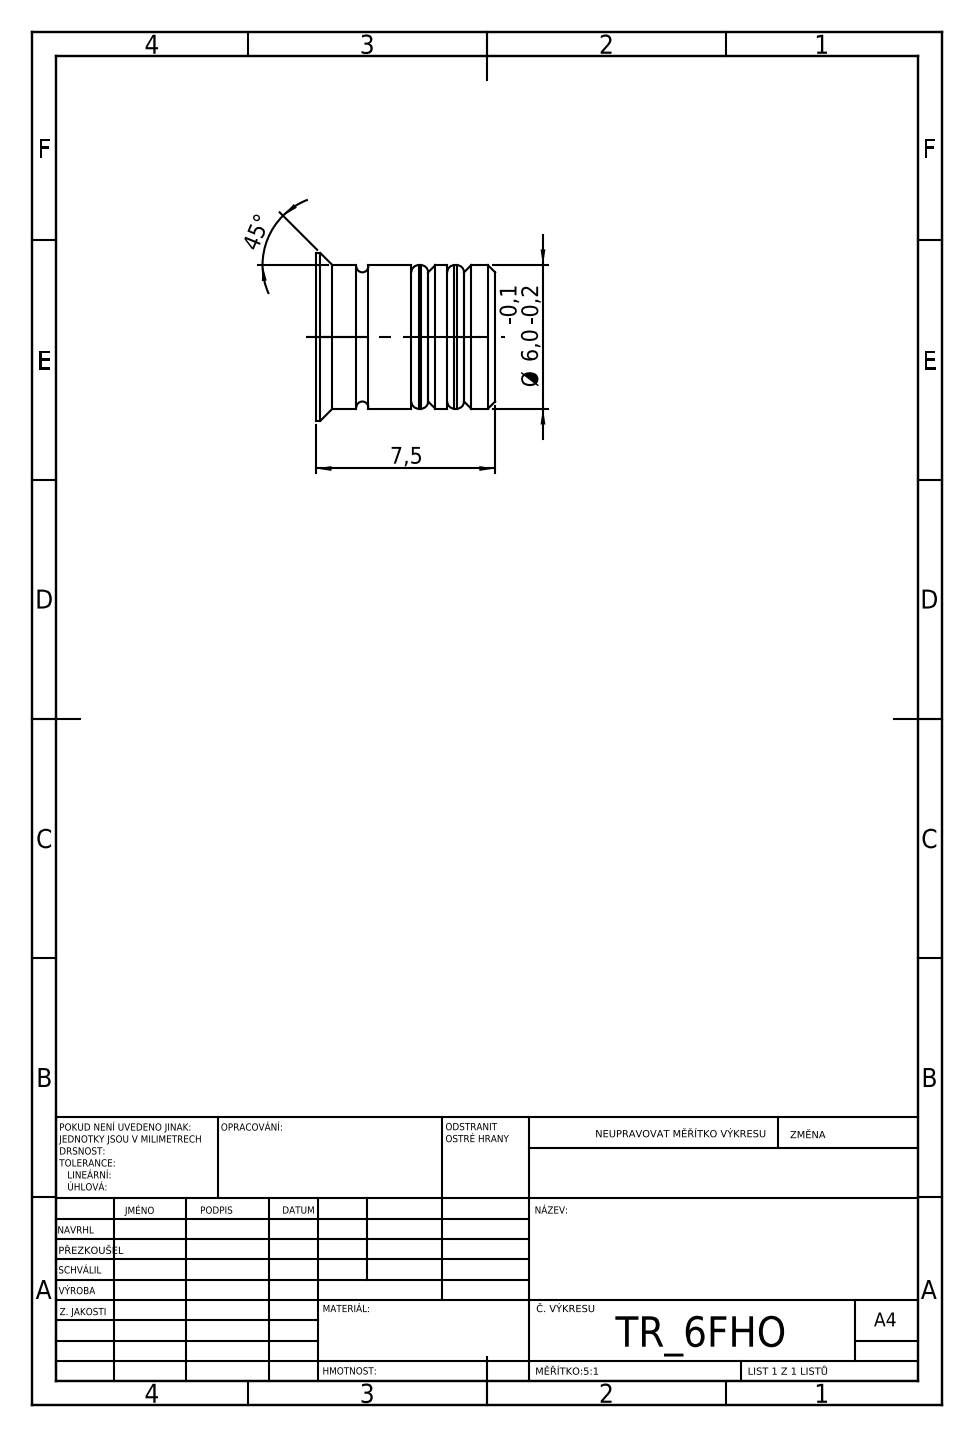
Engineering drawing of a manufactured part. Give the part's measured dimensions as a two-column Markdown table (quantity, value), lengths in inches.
| quantity | value |
| --- | --- |
| STEP written by | SolidWorks 2019 (CONFIG_CONTROL_DESIGN) |
| units | inches |
| bodies | 3 solids, 67 faces (25 planar, 20 cylindrical, 22 other) |
| overall size | 0.295 × 0.276 × 0.276 |
| volume | 0.014 in³ |
| surface area | 0.6 in² |
| round bosses / shafts (diameter × count) | 0.276 × 1, 0.236 × 1, 0.213 × 1, 0.118 × 1 |
| main face-to-face distances | 0.059, 0.028, 0.157, 0.079, 0.217, 0.087, 0.244, 0.031, 0.185, 0.051 |
